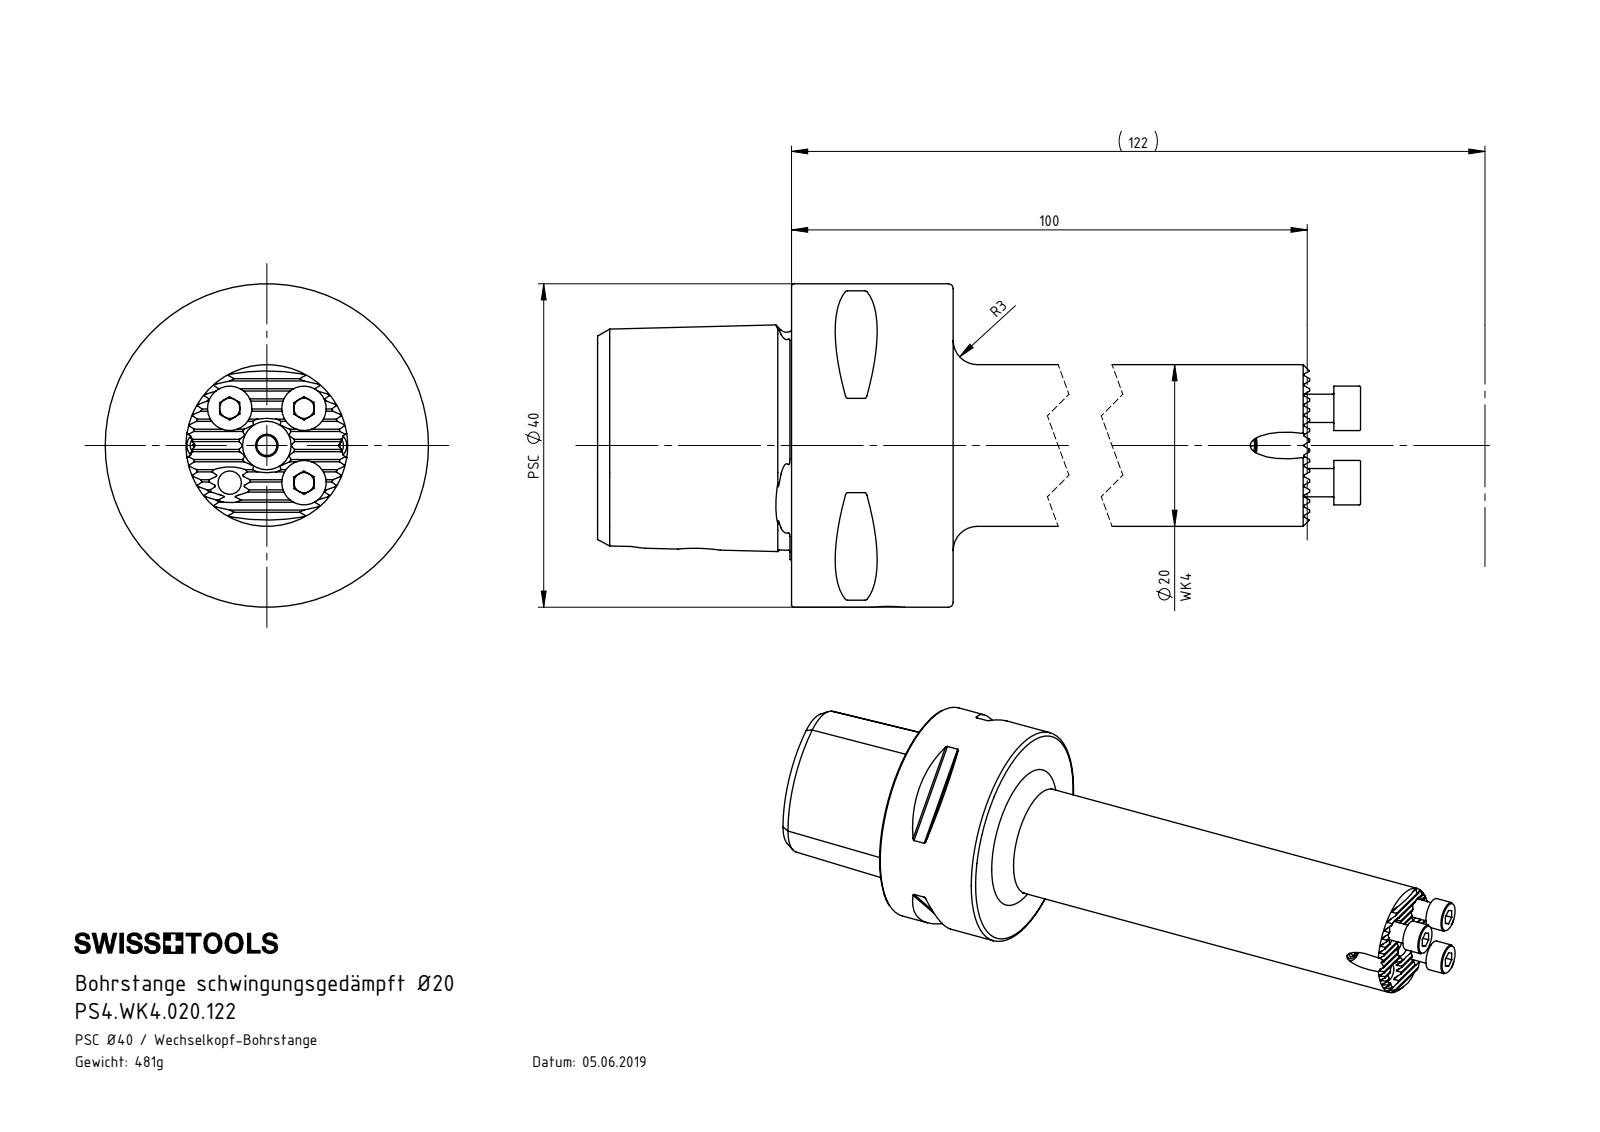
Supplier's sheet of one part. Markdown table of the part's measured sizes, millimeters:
| quantity | value |
| --- | --- |
| part name | ISO 4026 - M3 x 3; DIN 3771 - 6x1; ISCAR M3.5 x 10; PS4.WK4.020.122 (+3 more) |
| STEP written by | SolidWorks 2017 (AUTOMOTIVE_DESIGN) |
| units | millimeters |
| bodies | 9 solids, 356 faces (188 planar, 77 cylindrical, 91 other) |
| overall size | 130.6 × 40 × 40 |
| volume | 55 305 mm³ |
| surface area | 22 009 mm² |
| round holes (diameter × count) | 2.5 × 6, 2.9 × 4, 3.3 × 2, 3 × 1, 4 × 1, 4.6 × 1, 6 × 1, 6.8 × 1, 7.4 × 1, 12.5 × 1, 18 × 1, 20 × 1 |
| round bosses / shafts (diameter × count) | 5.5 × 3, 3.5 × 3, 3 × 2, 40 × 1, 12 × 1 |
| partial cylindrical surfaces (radius × count) | 0.12 × 15, 0.3 × 8, 3 × 1 |
| main face-to-face distances | 20, 78.5, 58.5, 24, 44, 102.5, 4.33, 1.5, 1.08, 3.25 |
| hole center spacings | 6.51, 9.2, 13.01, 23.5 |
